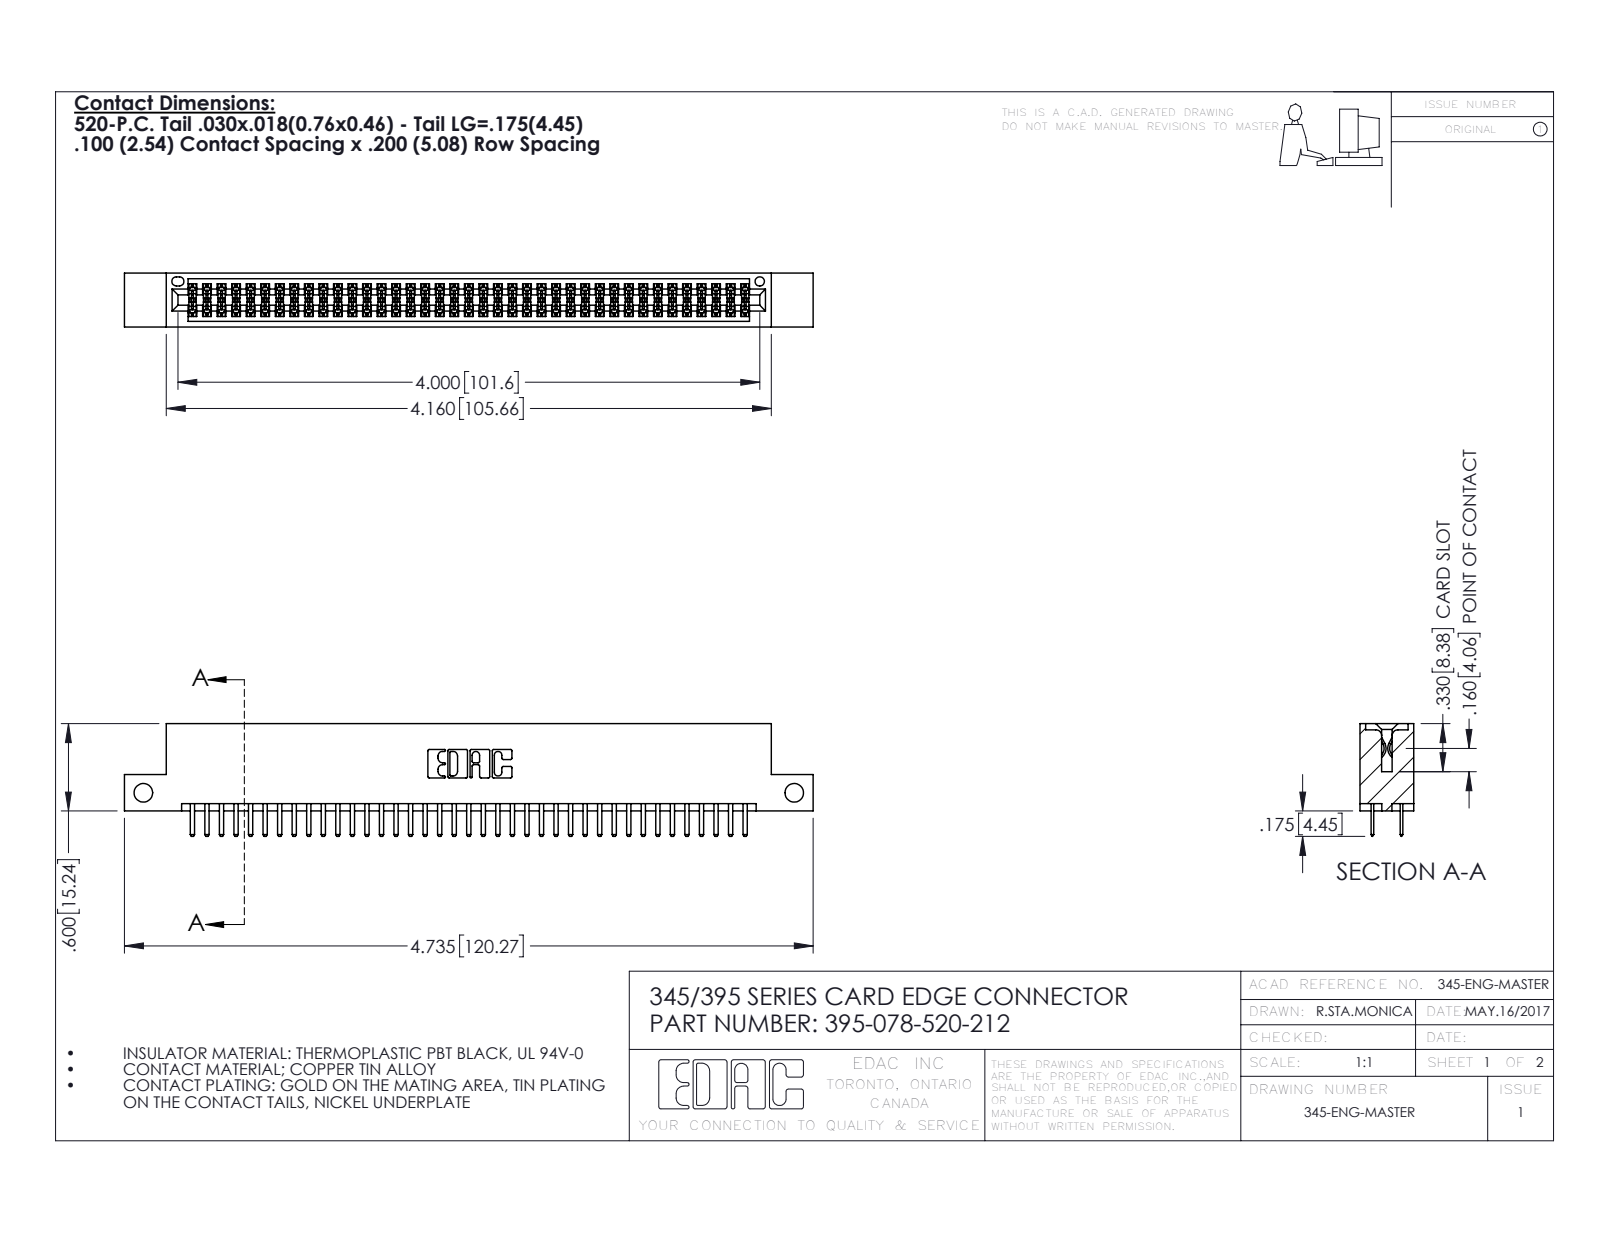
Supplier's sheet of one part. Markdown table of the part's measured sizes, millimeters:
| quantity | value |
| --- | --- |
| part name | 345 Part_Flush Mounting Lugs - Side Mount; 345-292-001_345-293-120; 395-078-520-212 |
| STEP written by | SolidWorks 2016 (CONFIG_CONTROL_DESIGN) |
| units | millimeters |
| bodies | 79 solids, 4338 faces (2810 planar, 1528 cylindrical, 0 other) |
| overall size | 120.3 × 19.7 × 9.4 |
| volume | 11 500 mm³ |
| surface area | 16 780 mm² |
| round holes (diameter × count) | 3.3 × 2, 1.6 × 1 |
| partial cylindrical surfaces (radius × count) | 0.2 × 117, 0.3 × 82, 0.3 × 22, 0.2 × 6, 0.8 × 6, 0.7 × 3, 0.4 × 2, 0.5 × 2 |
| main face-to-face distances | 7.6, 1.8, 5.1, 9.4, 2.5, 6.9, 0.6, 5.7, 0.6, 1.8 |
| hole center spacings | 113.7 |
